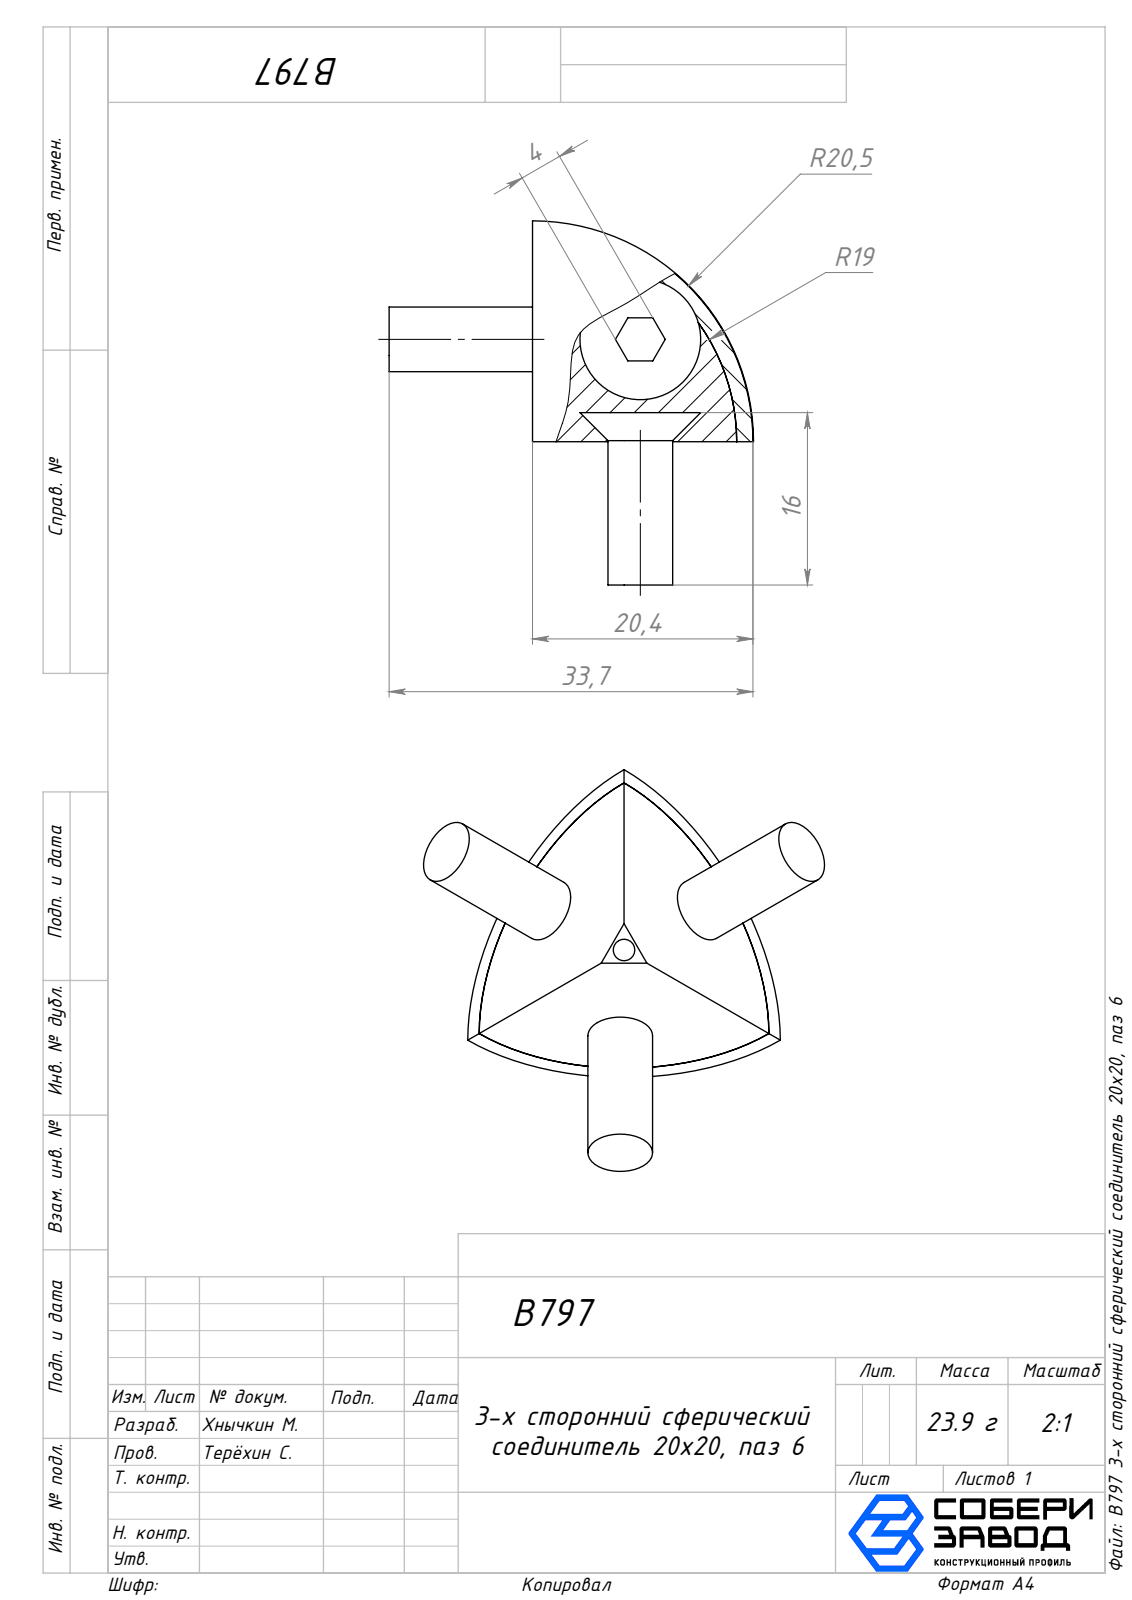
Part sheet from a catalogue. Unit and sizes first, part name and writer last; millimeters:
Units: millimetres
Overall size (bounding box): 33.8 × 33.8 × 33.8
Round holes (diameter × count): ⌀6 ×3, ⌀2 ×1
Round bosses / shafts (diameter × count): ⌀2 ×1
Main face-to-face distances: 2.7, 3, 13.3, 16, 16.3, 4, 13, 3.3, 4.5, 20.8
Volume: 3 919 mm³ · Surface area: 4 583 mm²
Bodies: 5 solids, 69 faces (38 planar, 16 cylindrical, 15 other)
Part name (STEP PRODUCT): B797 Крышка_00; B797 3-х сторонний сферический соединитель 20х20, паз 6; B797 Корпус_00; B797 Винт_00
STEP written by: SolidWorks 2025 (AUTOMOTIVE_DESIGN)
